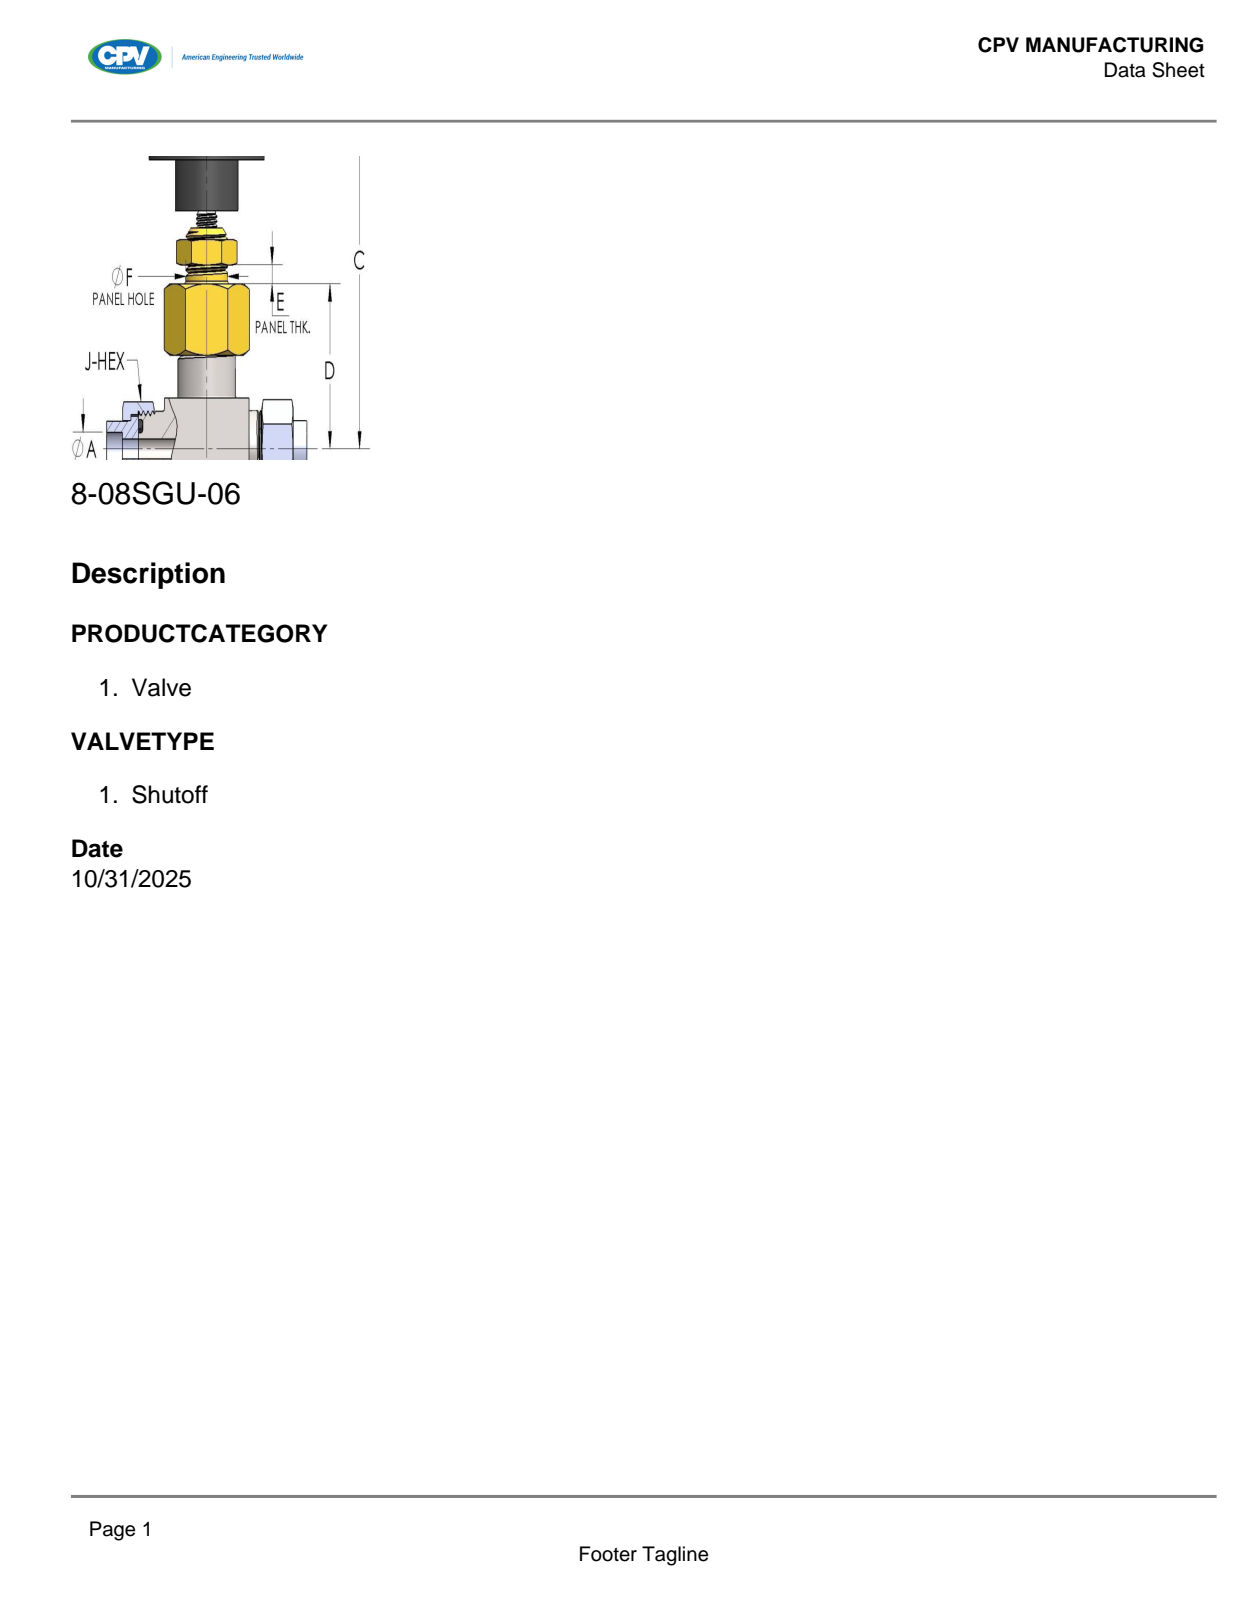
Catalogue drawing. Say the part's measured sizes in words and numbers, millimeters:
The part is named "8-08SGU-06". Its 3-D file was written by "SolidWorks 2018 (AUTOMOTIVE_DESIGN)". It is 1 solid with 175 faces: 58 planar, 43 cylindrical and 74 other. Overall it measures 95.7 by 82.8 by 47.8 millimeters. Its volume is 90 180 cubic millimeters and its surface area 21 440 square millimeters. Round holes: 1 of diameter 6.4, 1 of diameter 8.7, 1 of diameter 9.7. Round bosses or shafts: 1 of diameter 47.8, 1 of diameter 25.4, 1 of diameter 25.3, 1 of diameter 20.5, 1 of diameter 19, 1 of diameter 15, 1 of diameter 7.9, 1 of diameter 6.4. The main face-to-face distances are 28.6, 7.9, 87.8, 95.7, 12.7, 23.9, 2.4, 26.2, 2.4, 26.3.
